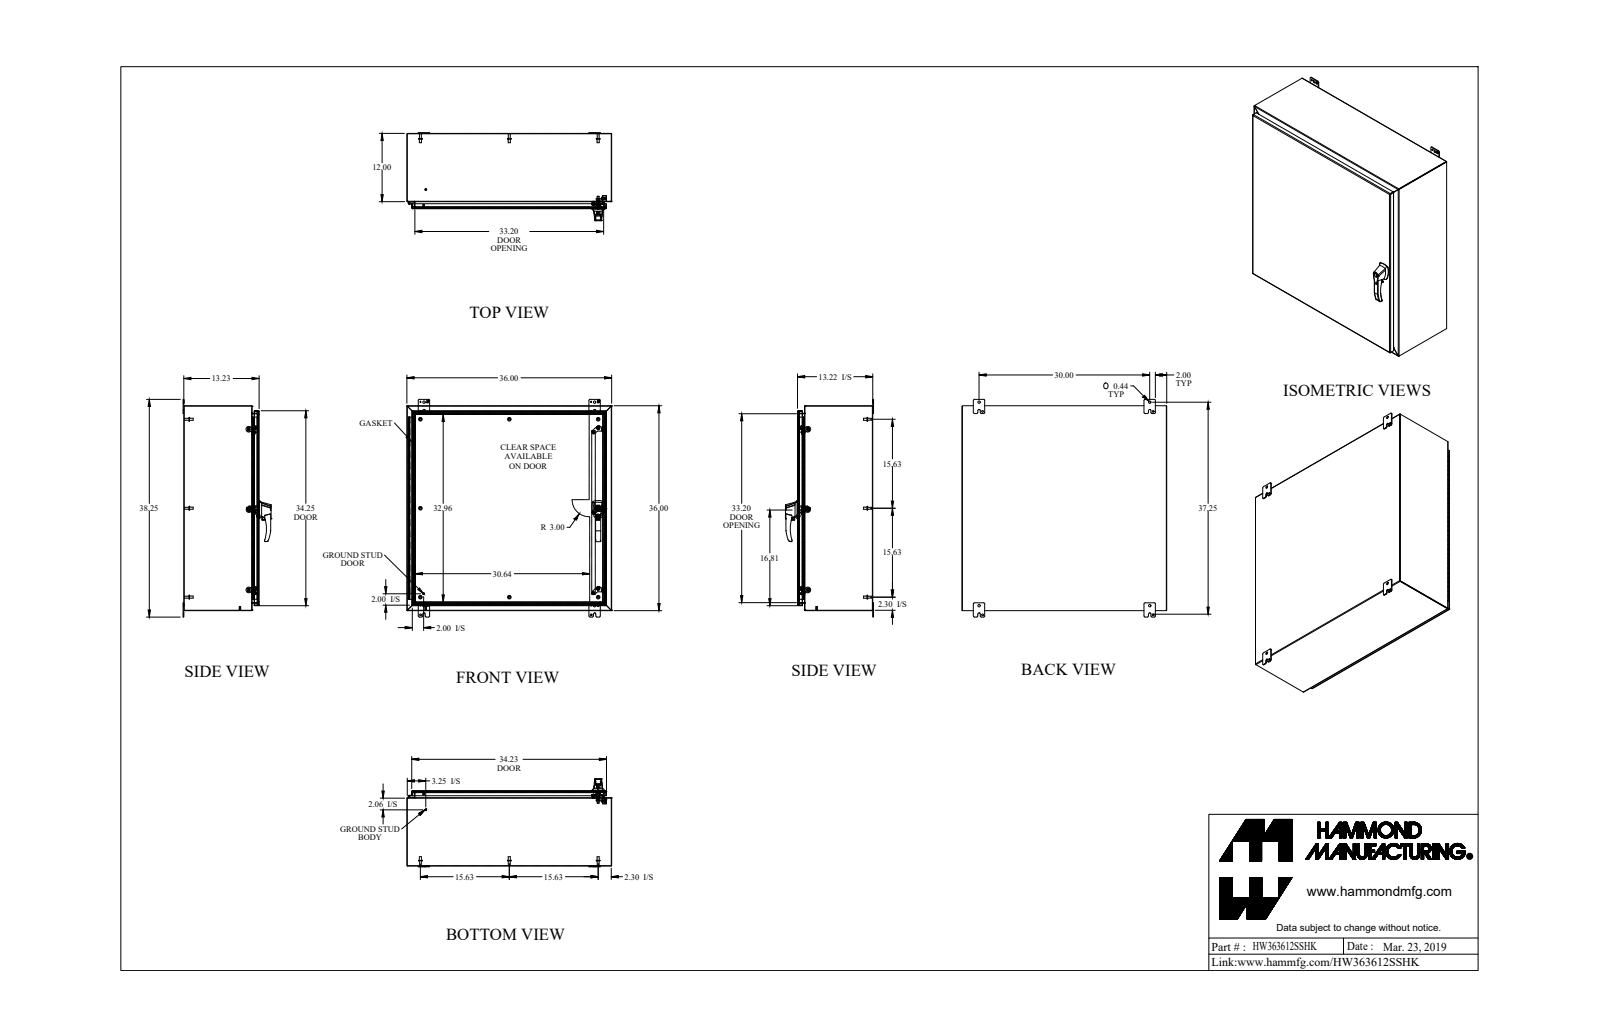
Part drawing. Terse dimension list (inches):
name: HW363612SSHK
written by: SolidWorks 2018 (AUTOMOTIVE_DESIGN)
unit: in
bodies: 48 solids, 1540 faces (729 planar, 641 cylindrical, 170 other)
size: 38.25 × 36 × 15.473
volume: 405.6 in³; area: 10 029 in²
holes: 6× ⌀0.176, 5× ⌀0.313, 3× ⌀0.25, 3× ⌀0.265, 3× ⌀0.413, 2× ⌀0.196, 2× ⌀0.256, 2× ⌀0.394, 2× ⌀0.437, 1× ⌀0.187, 1× ⌀0.233, 1× ⌀0.33
bosses: 13× ⌀0.375, 8× ⌀0.65, 8× ⌀0.332, 7× ⌀0.25, 6× ⌀0.156, 3× ⌀1, 3× ⌀0.51, 3× ⌀0.313
rounds: 27× R0.25, 24× R0.188, 14× R0.036, 14× R0.108, 12× R0.06, 9× R0.125, 8× R0.045, 8× R0.218
face distances: 0.072, 35.928, 13.138, 13.066, 0.095, 13.233, 13.161, 35.856, 36, 11.928
hole spacings: 14.118, 14.119, 28.237, 1.11, 1.111, 1.338, 12.78, 14.119
